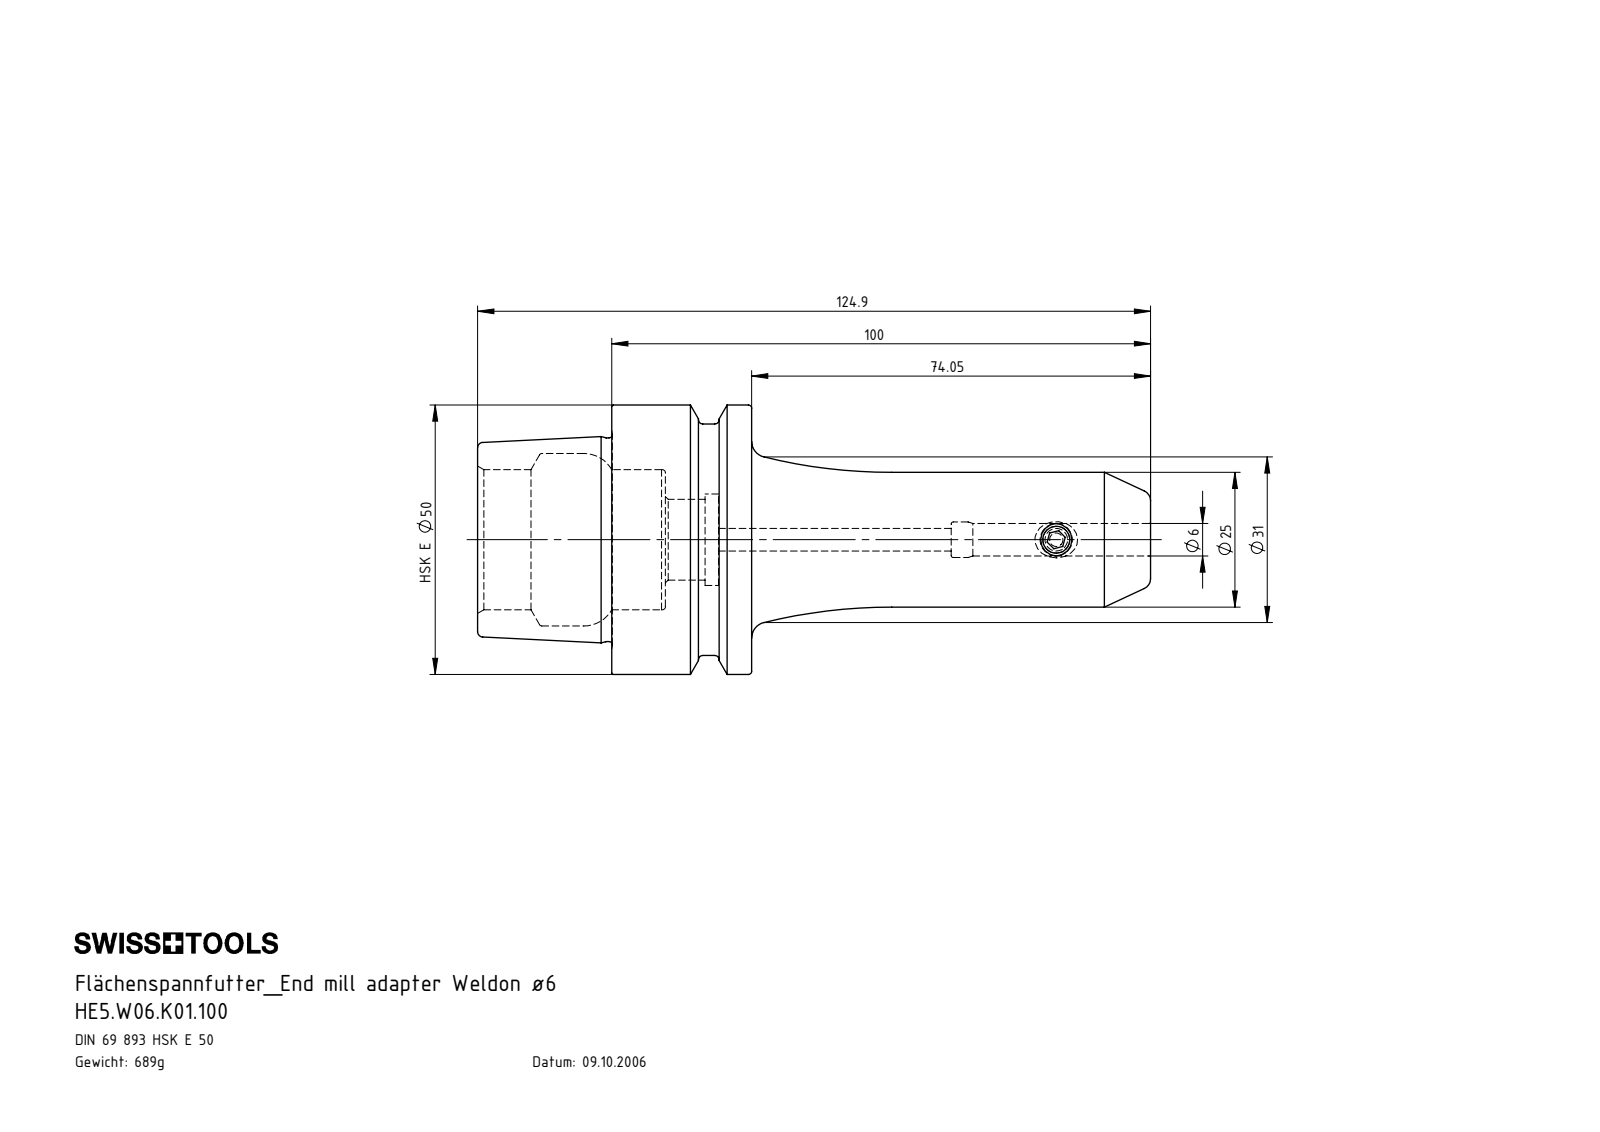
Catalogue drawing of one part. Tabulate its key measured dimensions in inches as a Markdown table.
| quantity | value |
| --- | --- |
| part name | HE5.W06.K01.100; HE5-W06.K01.100_B_Fertigbearbeitung; W06-ER1.001.010 |
| STEP written by | SolidWorks 2017 (AUTOMOTIVE_DESIGN) |
| units | inches |
| bodies | 2 solids, 111 faces (19 planar, 30 cylindrical, 62 other) |
| overall size | 4.917 × 1.969 × 1.969 |
| volume | 5.359 in³ |
| surface area | 34.11 in² |
| round holes (diameter × count) | 0.165 × 1, 0.197 × 1, 0.236 × 1, 0.26 × 1, 0.591 × 1, 0.669 × 1, 1.024 × 1, 1.26 × 1 |
| round bosses / shafts (diameter × count) | 1.969 × 1, 1.691 × 1, 1.489 × 1, 0.984 × 1, 0.236 × 1 |
| main face-to-face distances | 1.022, 0.98, 2.002, 1.372, 0.392, 0.63, 1.76, 0.78, 0.388, 0.242 |
